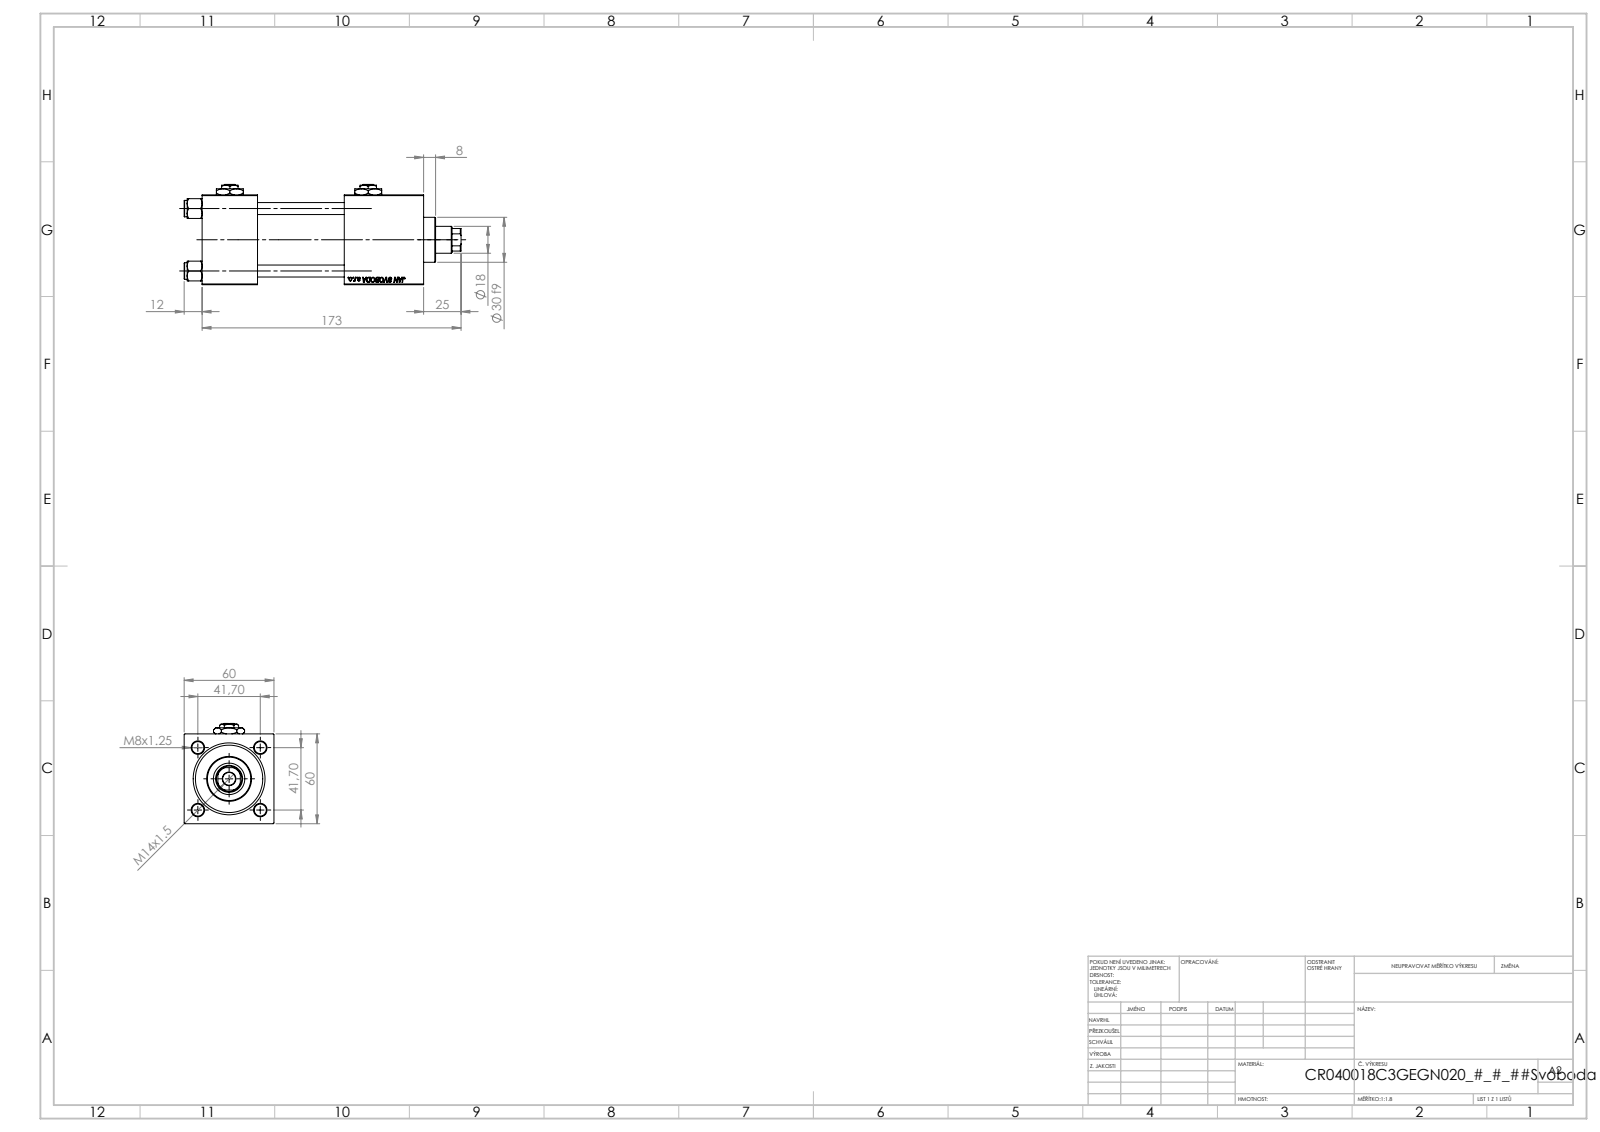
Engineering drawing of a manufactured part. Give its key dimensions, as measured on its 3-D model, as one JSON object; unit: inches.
{"part_name": "NUT_M5_C; V215CR_VCP_C; V215CR_C_TYCINKA; V215_VC_A (+2 more)", "step_written_by": "SolidWorks 2019 (CONFIG_CONTROL_DESIGN)", "units": "inches", "bodies": {"solids": 13, "faces": 1250, "planar": 574, "cylindrical": 98, "other": 578}, "overall_size": [7.283, 2.638, 2.362], "volume_in3": 24.34, "surface_area_in2": 167.9, "round_holes": [[0.315, 4], [0.276, 2], [0.656, 2], [0.945, 2], [0.335, 1], [0.709, 1], [0.827, 1], [1.22, 1], [1.575, 1], [1.772, 1]], "round_bosses_or_shafts": [[0.433, 4], [1.811, 1], [1.181, 1]], "partial_cylinders_radius": [[0.335, 1]], "face_to_face_distances": [2.362, 1.457, 2.087, 5.827, 4.37, 2.283, 3.74, 4.697, 3.24, 0.957], "hole_center_spacings": [1.161, 1.642, 2.322, 3.642]}
